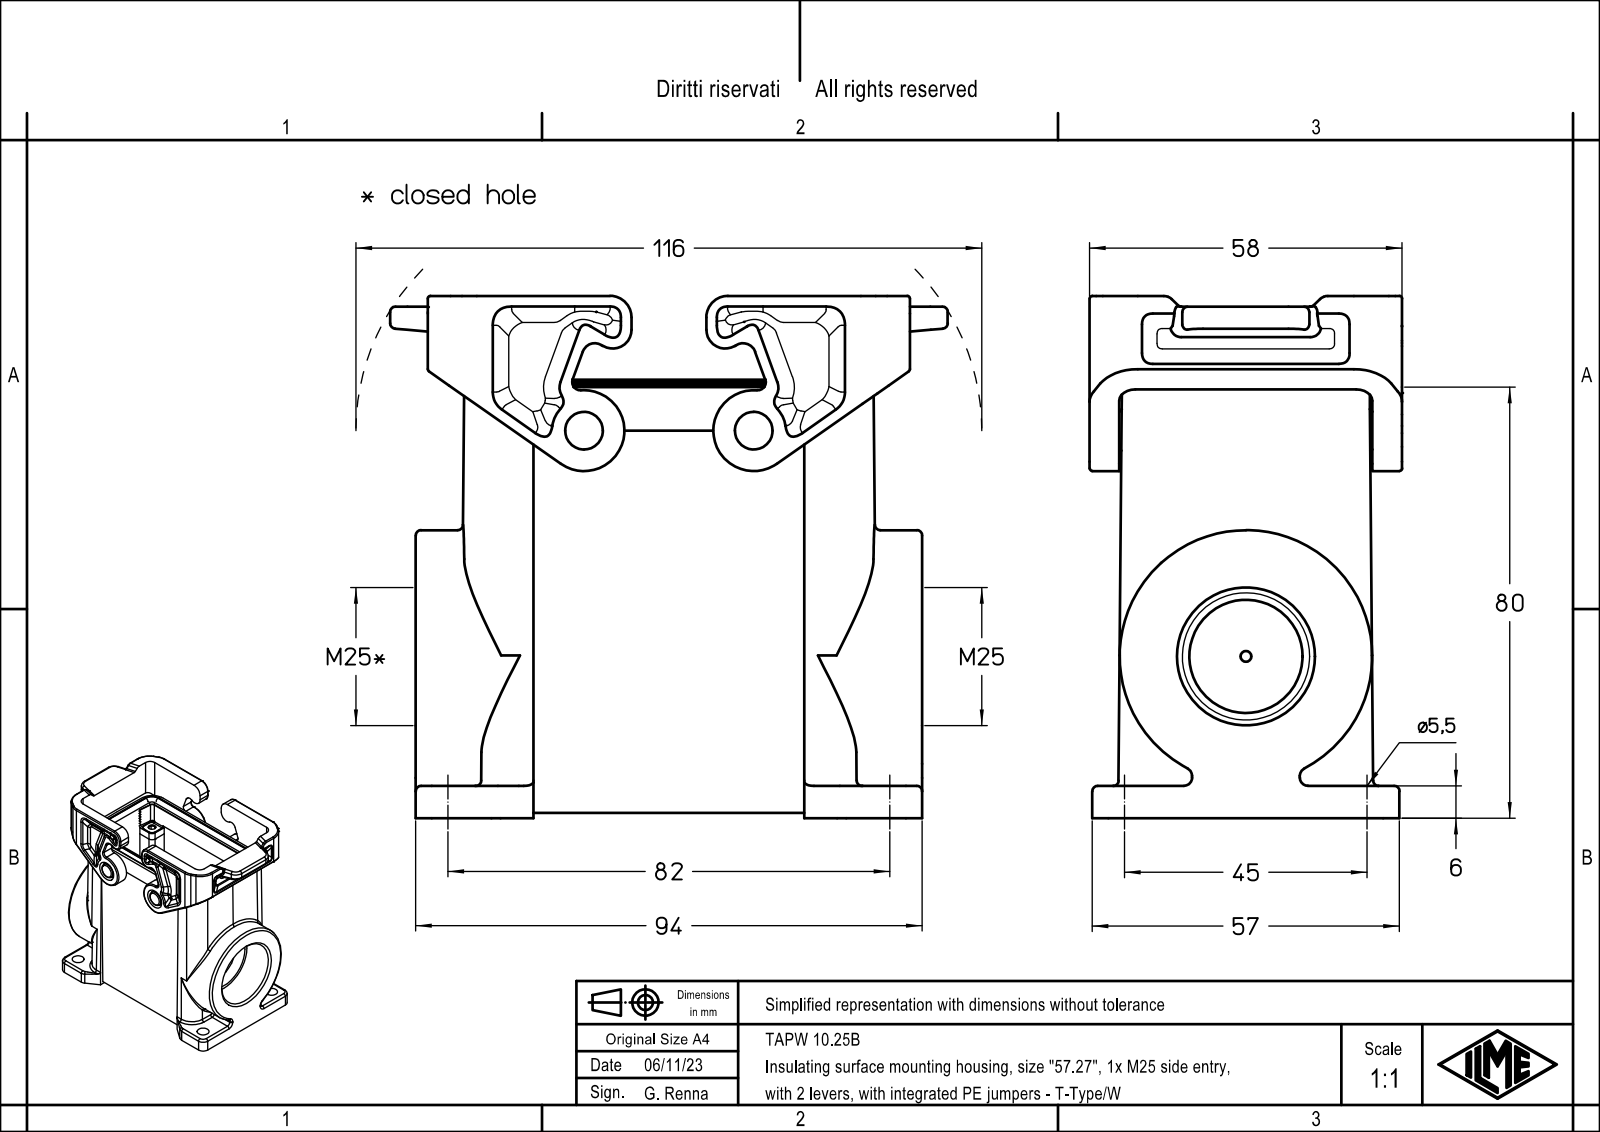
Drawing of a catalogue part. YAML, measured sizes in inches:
part_name: "TAPW 10.25B"
step_written_by: "Creo Elements/Direct Modeling 20.1B 02-Apr-2019 (C) Parametric Technology GmbH (AUTOMOTIVE_DESIGN)"
units: inches
bodies: {solids: 1, faces: 606, planar: 360, cylindrical: 194, other: 52}
overall_size: [4.075, 3.815, 2.283]
volume: 11.28
surface_area: 98.46
round_holes:
  - {diameter: 0.138, count: 4}
  - {diameter: 0.217, count: 4}
  - {diameter: 0.827, count: 1}
  - {diameter: 0.929, count: 1}
round_bosses_or_shafts:
  - {diameter: 0.276, count: 2}
  - {diameter: 1.845, count: 1}
partial_cylinders:
  - {radius: 0.079, count: 20}
  - {radius: 0.118, count: 20}
  - {radius: 0.059, count: 18}
  - {radius: 0.039, count: 16}
  - {radius: 0.051, count: 12}
  - {radius: 0.236, count: 8}
  - {radius: 0.276, count: 8}
  - {radius: 0.157, count: 6}
face_to_face_distances: [1.386, 0.217, 0.232, 1.618, 0.039, 0.256, 0.449, 1.835, 2.067, 3.701]
hole_center_spacings: [0.606, 1.5, 2.759, 3.081, 1.063, 1.772, 2.244, 2.483]
